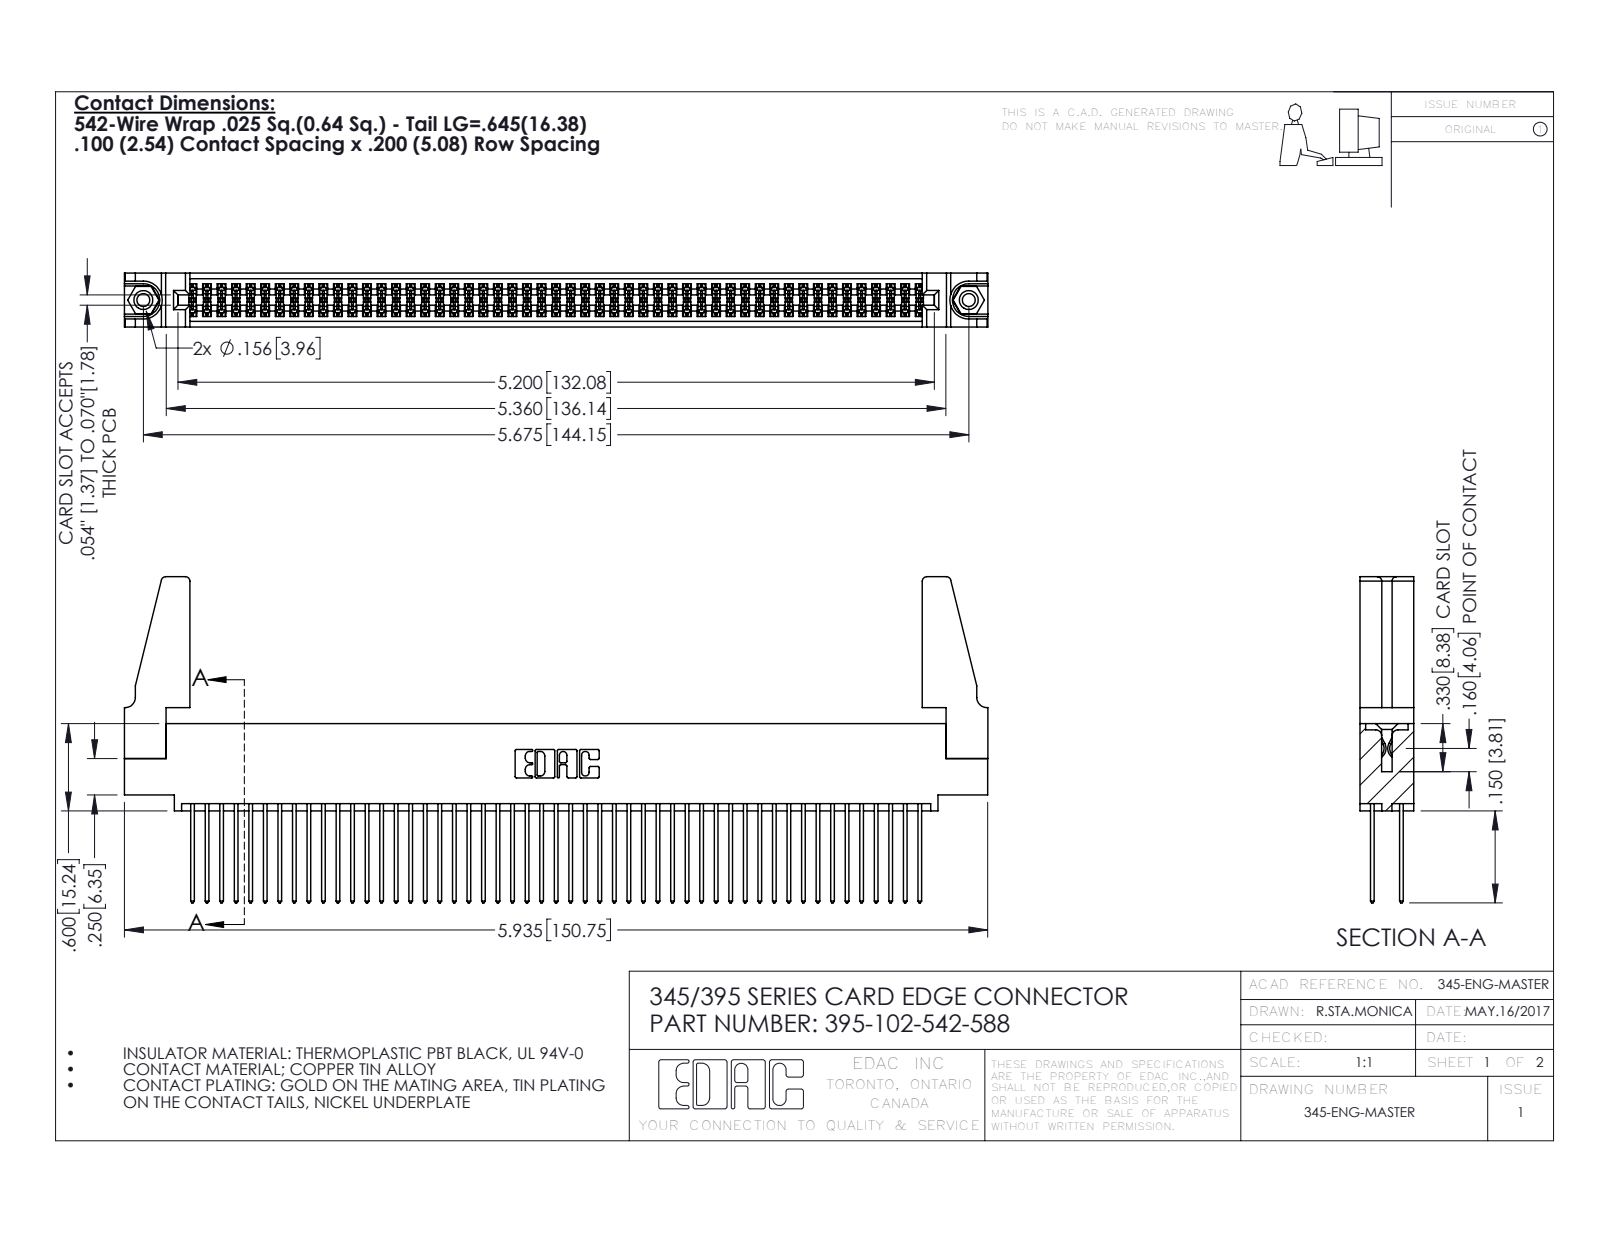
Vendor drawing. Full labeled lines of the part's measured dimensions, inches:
Part name (STEP PRODUCT): 345-292-001_345-293-142; 345-220-078_345-220-088; 345 Part_0.110 Offset - 0.156 Dia-TH; 345-250-001_345-250-001-102 (+1 more)
STEP written by: SolidWorks 2016 (CONFIG_CONTROL_DESIGN)
Units: inches
Bodies: 107 solids, 5354 faces (3522 planar, 1816 cylindrical, 16 other)
Overall size (bounding box): 5.936 × 2.242 × 0.37
Volume: 1.122 in³ · Surface area: 43.37 in²
Round holes (diameter × count): ⌀0.089 ×2, ⌀0.125 ×2, ⌀0.156 ×2, ⌀0.064 ×1
Round bosses / shafts (diameter × count): ⌀0.155 ×2
Partial cylindrical surfaces — rounded edges, fillets, slot ends (radius × count): R0.006 ×153, R0.01 ×102, R0.01 ×22, R0.03 ×8, R0.007 ×6, R0.031 ×6, R0.026 ×3, R0.014 ×2
Main face-to-face distances: 0.072, 0.298, 0.2, 0.098, 0.272, 0.025, 0.37, 0.225, 0.175, 0.149
Hole centre spacings: 0.27, 5.439, 5.675
